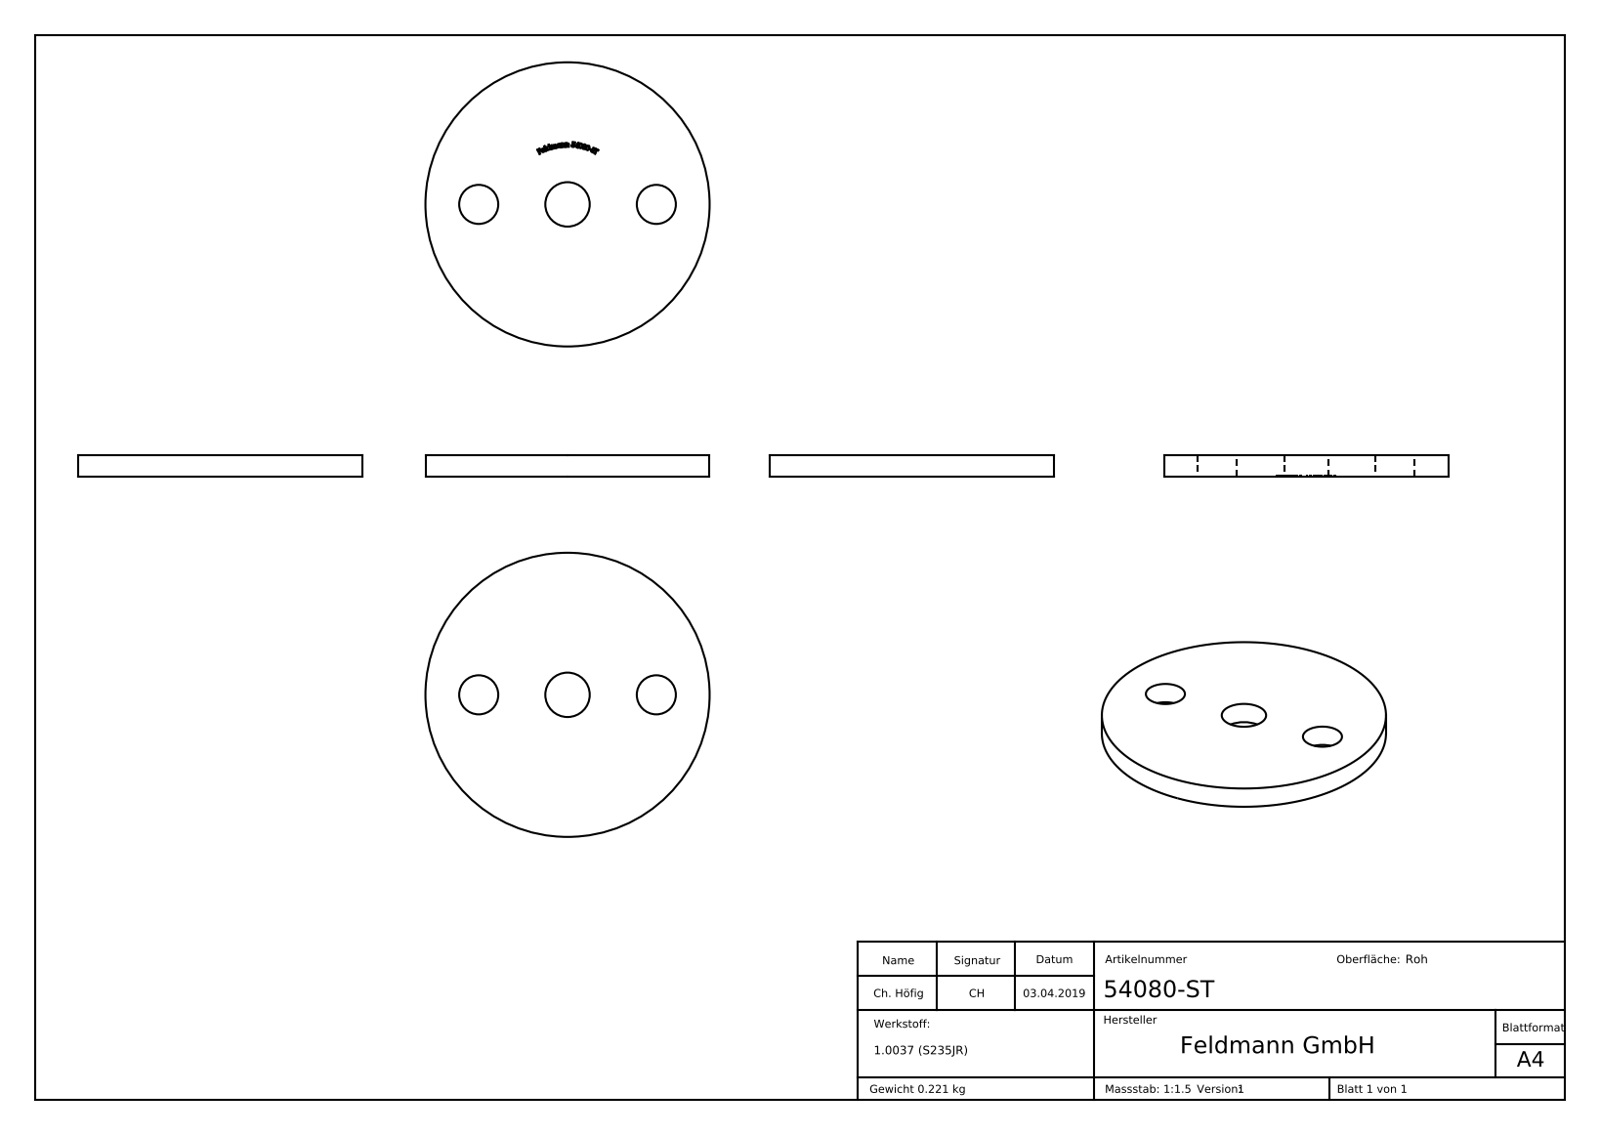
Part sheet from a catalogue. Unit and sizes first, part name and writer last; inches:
Units: inches
Overall size (bounding box): 3.15 × 3.15 × 0.236
Round holes (diameter × count): ⌀0.433 ×2, ⌀0.492 ×1
Round bosses / shafts (diameter × count): ⌀3.15 ×1
Main face-to-face distances: 0.236, 0.232, 0.021, 0.026, 0.026, 0.033, 0.028, 0.031, 0.052, 0.029
Hole centre spacings: 0.984, 1.969
Volume: 1.726 in³ · Surface area: 17.97 in²
Bodies: 1 solid, 227 faces (113 planar, 8 cylindrical, 106 other)
Part name (STEP PRODUCT): 54080-ST
STEP written by: SolidWorks 2015 (CONFIG_CONTROL_DESIGN)
